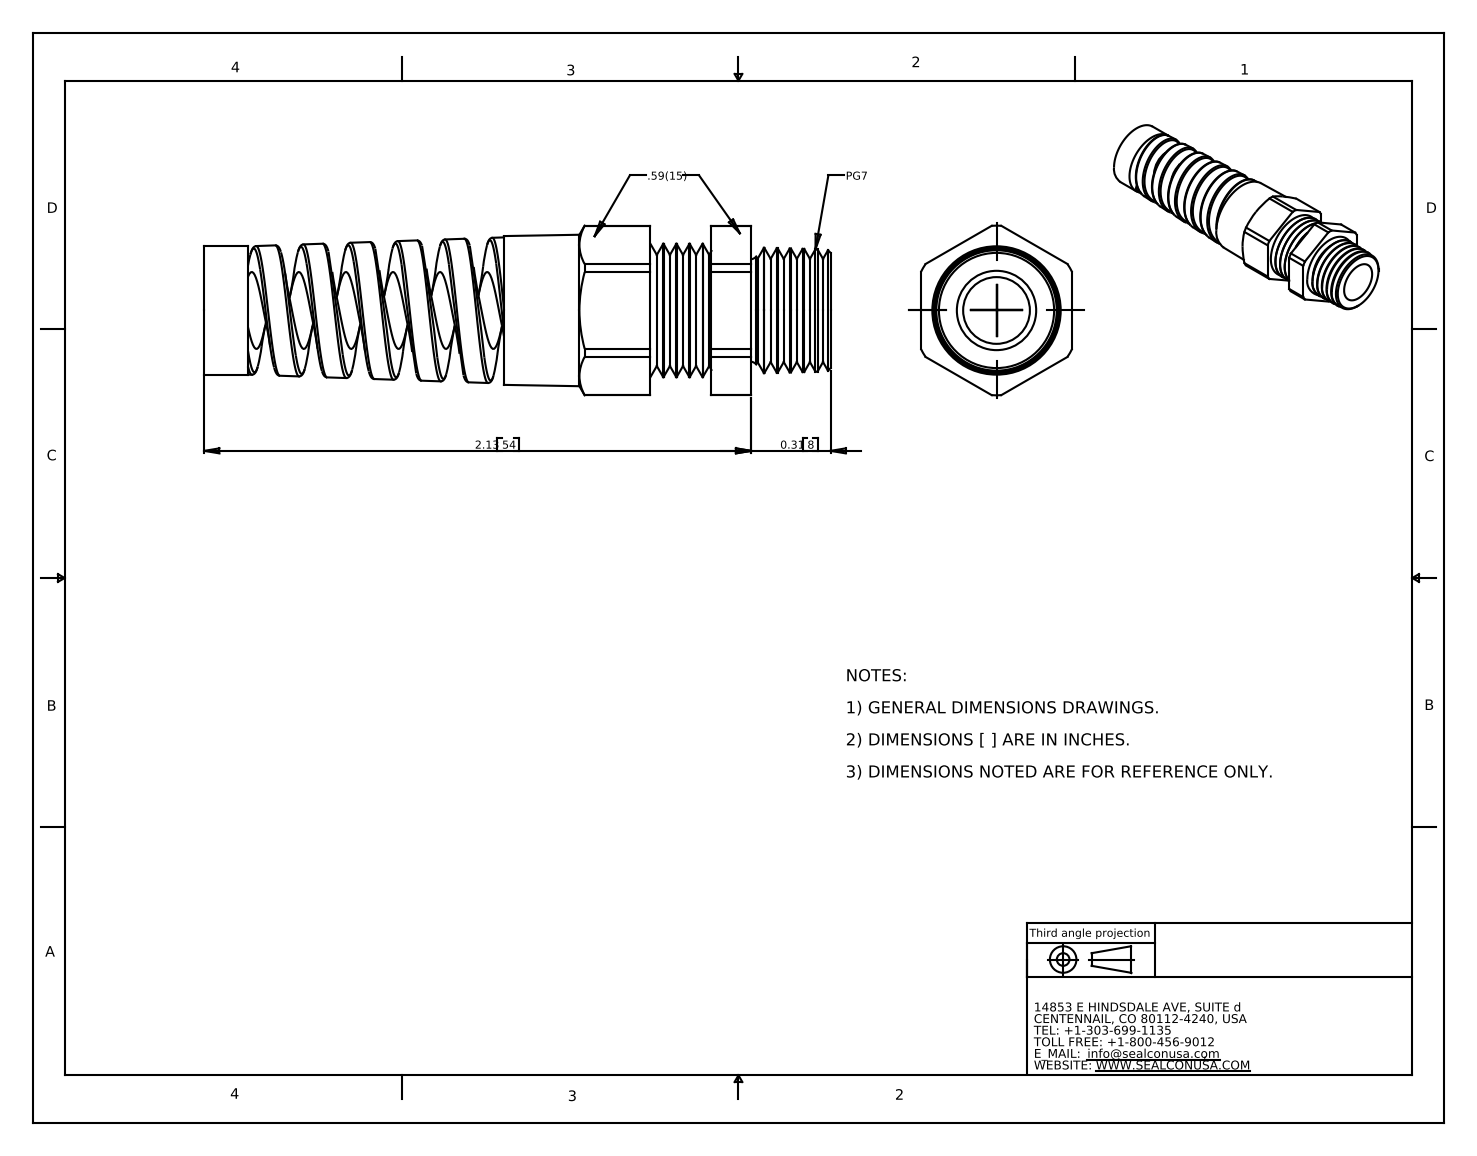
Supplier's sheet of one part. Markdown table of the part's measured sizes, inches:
| quantity | value |
| --- | --- |
| part name | CF07AA-GY |
| STEP written by | SolidWorks 2007 (CONFIG_CONTROL_DESIGN) |
| units | inches |
| bodies | 1 solid, 146 faces (19 planar, 39 cylindrical, 88 other) |
| overall size | 2.44 × 0.661 × 0.59 |
| volume | 0.327 in³ |
| surface area | 8.34 in² |
| round holes (diameter × count) | 0.26 × 1, 0.3 × 1 |
| round bosses / shafts (diameter × count) | 0.519 × 1, 0.5 × 1 |
| partial cylindrical surfaces (radius × count) | 0.33 × 1 |
| main face-to-face distances | 0.59, 2.13, 1.167, 0.963, 1.976, 0.808, 0.154, 1.738, 0.57, 0.238 |
